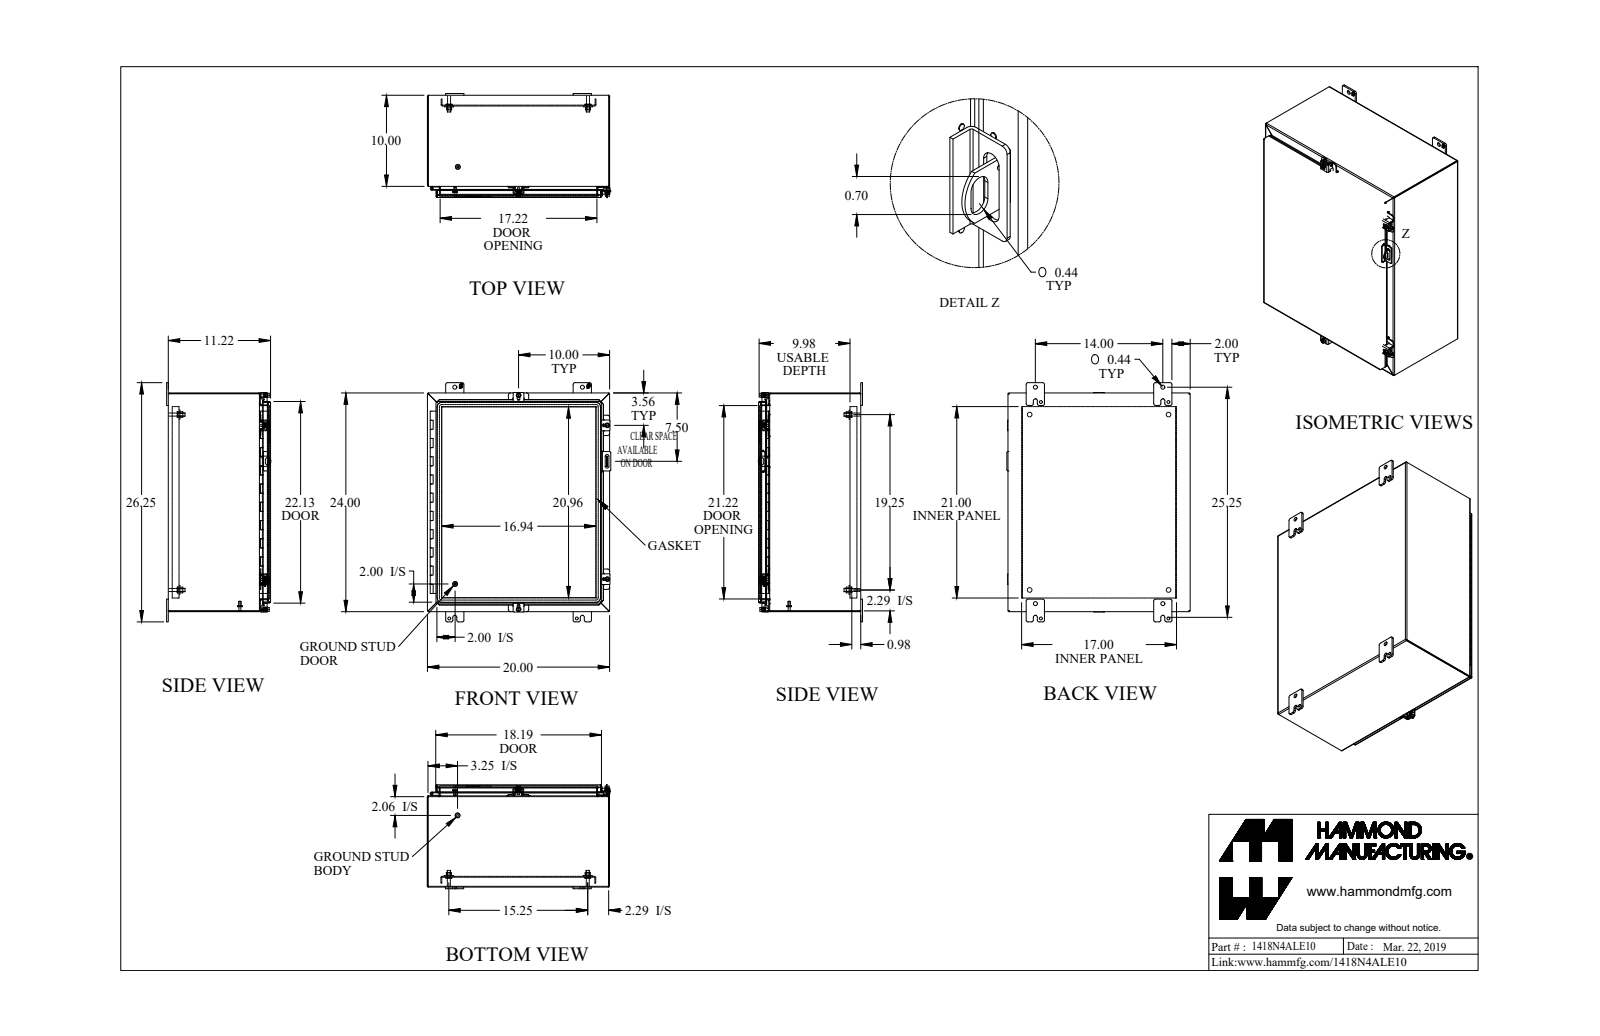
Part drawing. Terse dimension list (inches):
name: 1418N4ALE10_Default
written by: SolidWorks 2019 (CONFIG_CONTROL_DESIGN)
unit: in
bodies: 38 solids, 1524 faces (899 planar, 515 cylindrical, 110 other)
size: 26.25 × 20.126 × 11.438
volume: 224.8 in³; area: 5 207 in²
holes: 4× ⌀0.232, 4× ⌀0.313, 4× ⌀0.375, 4× ⌀0.437, 4× ⌀0.5, 2× ⌀0.265, 2× ⌀0.265, 2× ⌀0.307, 2× ⌀0.445, 1× ⌀0.125, 1× ⌀0.187
bosses: 12× ⌀0.131, 4× ⌀0.65, 4× ⌀0.5, 4× ⌀0.4, 4× ⌀0.375, 4× ⌀0.33, 4× ⌀0.244, 2× ⌀1
rounds: 24× R0.188, 22× R0.05, 22× R0.15, 20× R0.25, 16× R0.041, 16× R0.122, 10× R0.125, 8× R0.141
face distances: 0.081, 19.919, 0.1, 11.041, 11.122, 11.141, 11.222, 23.919, 0.095, 10.046
hole spacings: 14, 22.694, 7.915, 7.916, 15.25, 17.415, 24.559, 1.625
